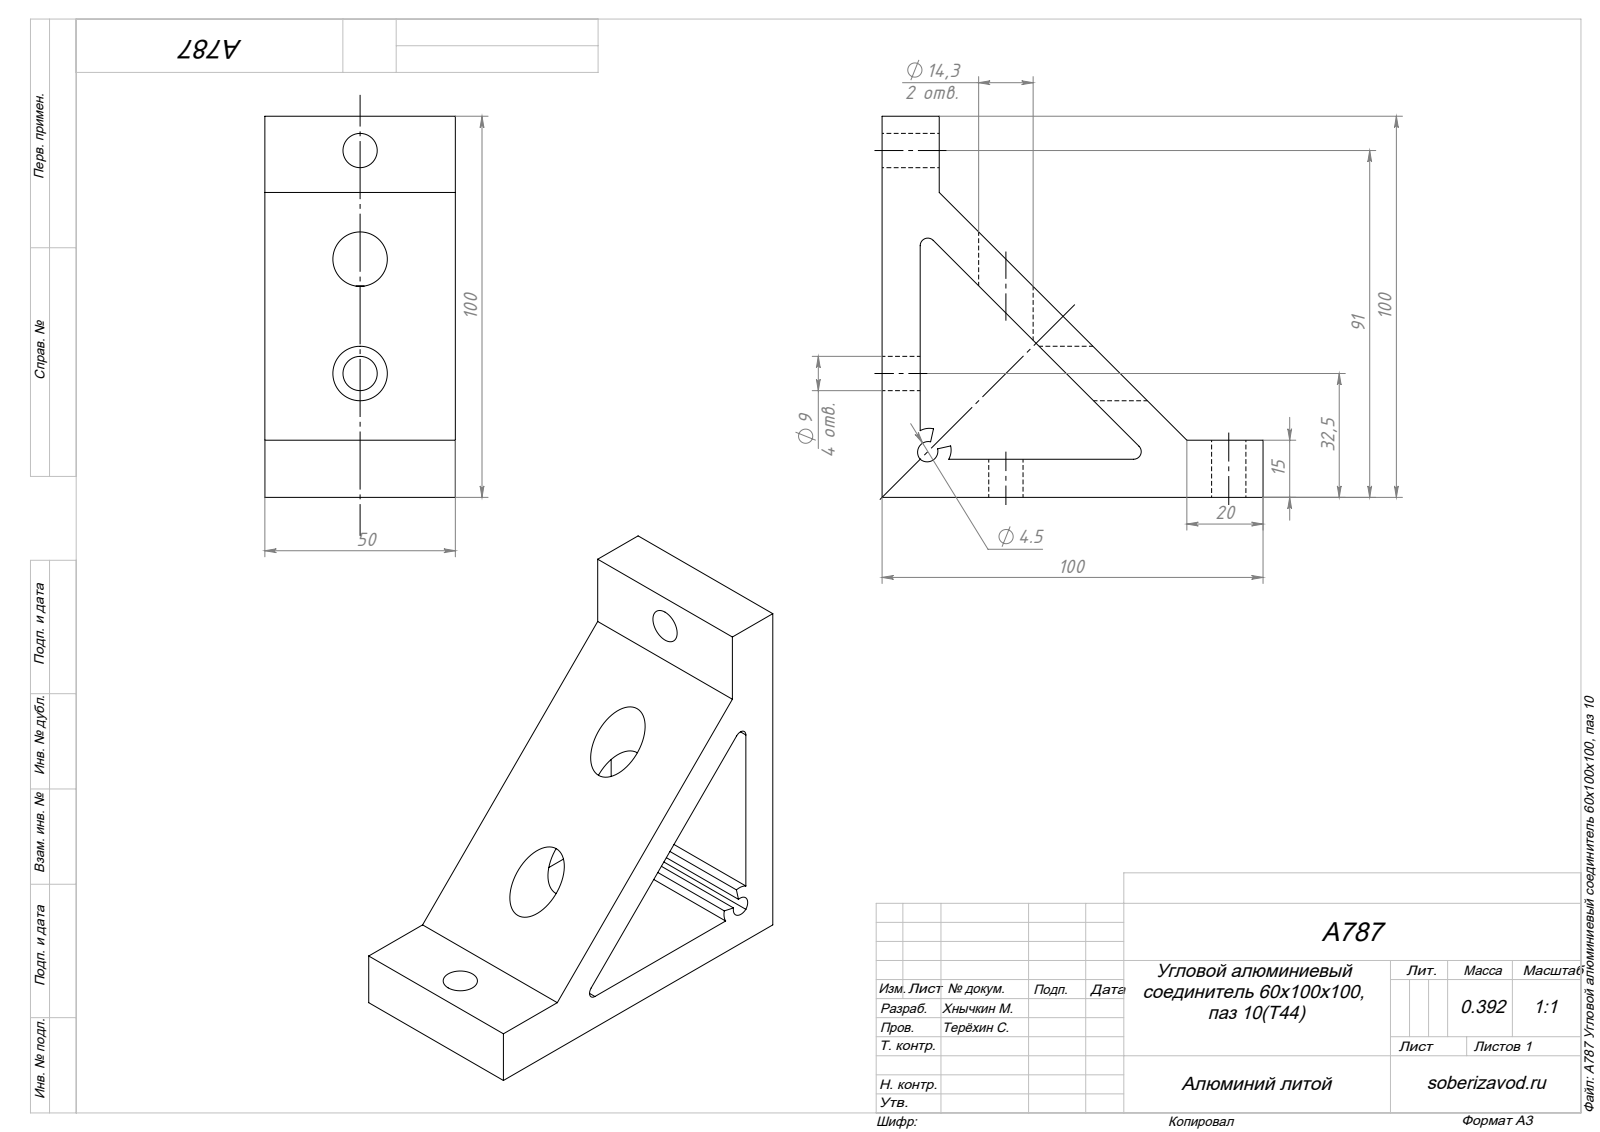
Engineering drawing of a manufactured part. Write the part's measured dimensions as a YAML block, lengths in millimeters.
part_name: "A787 Угловой алюминиевый соединитель 60х100х100, паз 10"
step_written_by: "SolidWorks 2025 (AUTOMOTIVE_DESIGN)"
units: millimeters
bodies: {solids: 1, faces: 34, planar: 14, cylindrical: 20, other: 0}
overall_size: [100, 100, 50]
volume: 145482
surface_area: 36051
round_holes:
  - {diameter: 9, count: 4}
  - {diameter: 14.3, count: 2}
partial_cylinders:
  - {radius: 2, count: 2}
  - {radius: 2.81, count: 2}
  - {radius: 5, count: 2}
face_to_face_distances: [10, 50, 15, 5, 100, 90, 85]
hole_center_spacings: [58.5]
